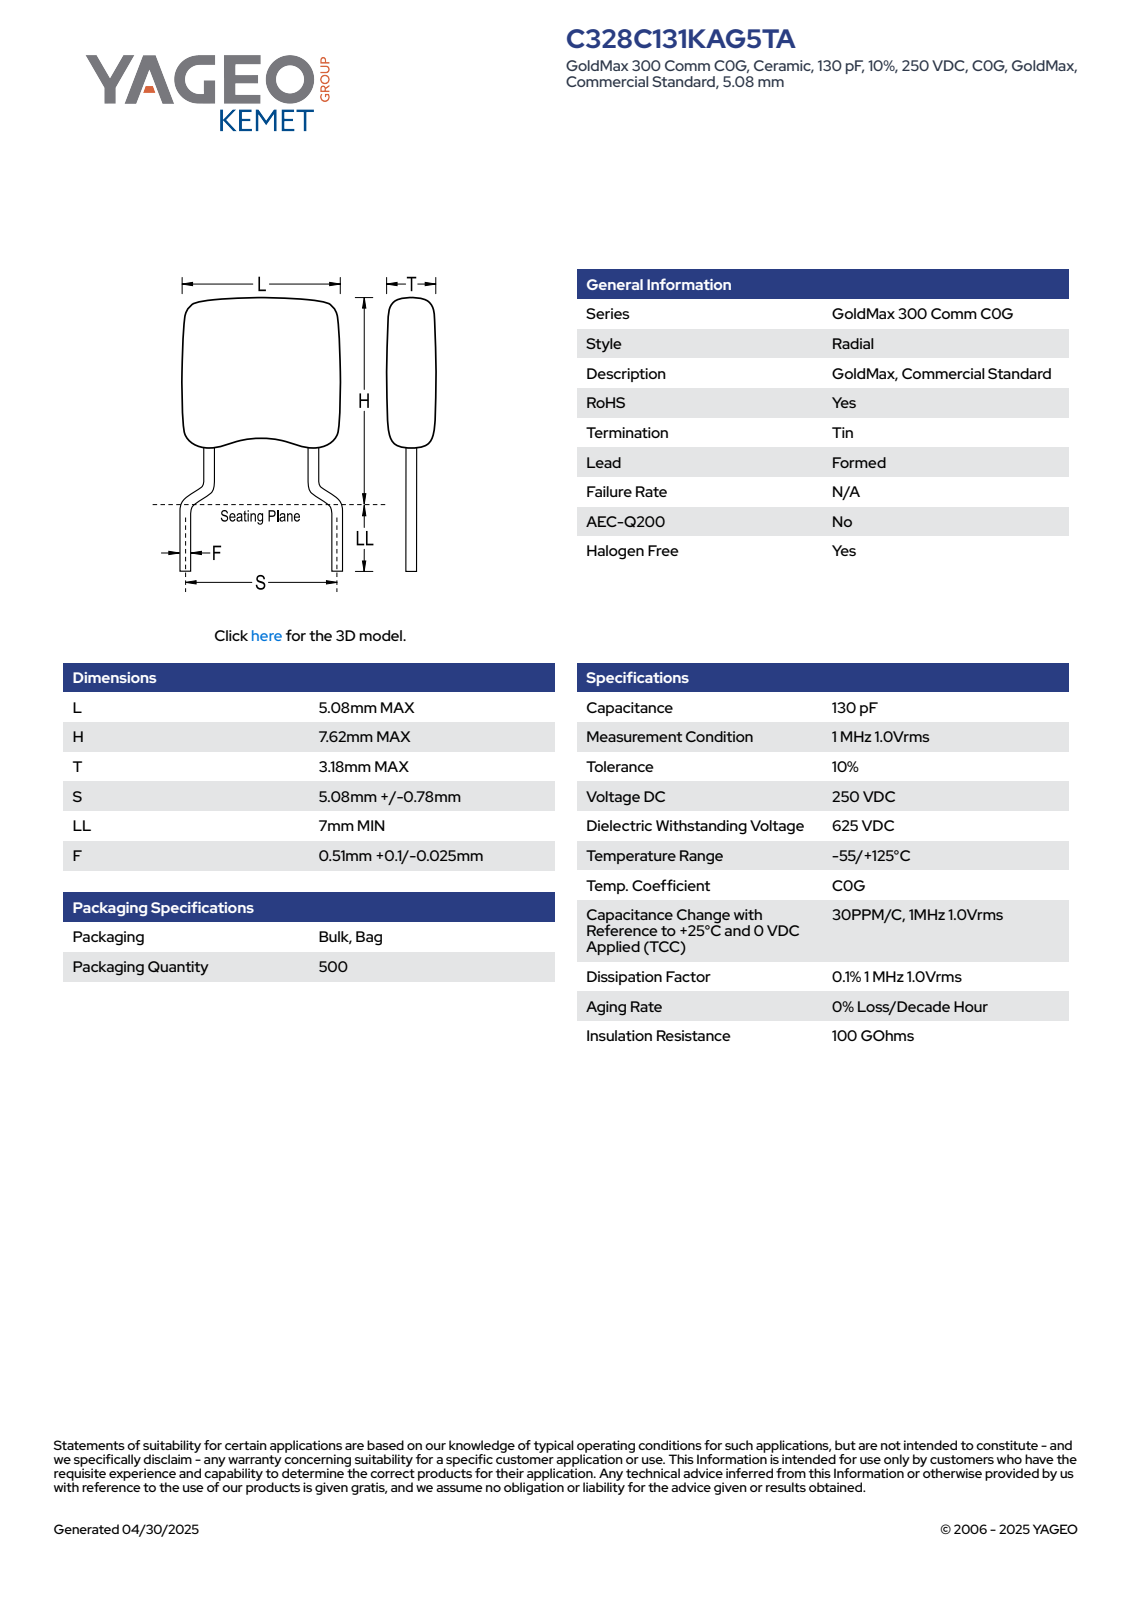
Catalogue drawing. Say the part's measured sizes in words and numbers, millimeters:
The part is named "CCRC328_L5.08H7.62T3.18S5.08LL7F0.61". Its 3-D file was written by "SolidWorks 2014 (AUTOMOTIVE_DESIGN)". It is 4 solids with 109 faces: 68 planar, 22 cylindrical and 19 other. Overall it measures 14.62 by 5.69 by 3.19 millimeters. Its volume is 76 cubic millimeters and its surface area 134 square millimeters. Round bosses or shafts: 6 of diameter 0.61. Partial cylindrical surfaces (rounded edges, fillets, slot ends): 8 of radius 0.75, 2 of radius 1. The main face-to-face distances are 3.18, 5.08, 4.81, 9.81, 14.62, 3.19, 0.43, 12.45, 2.64, 2.17.
